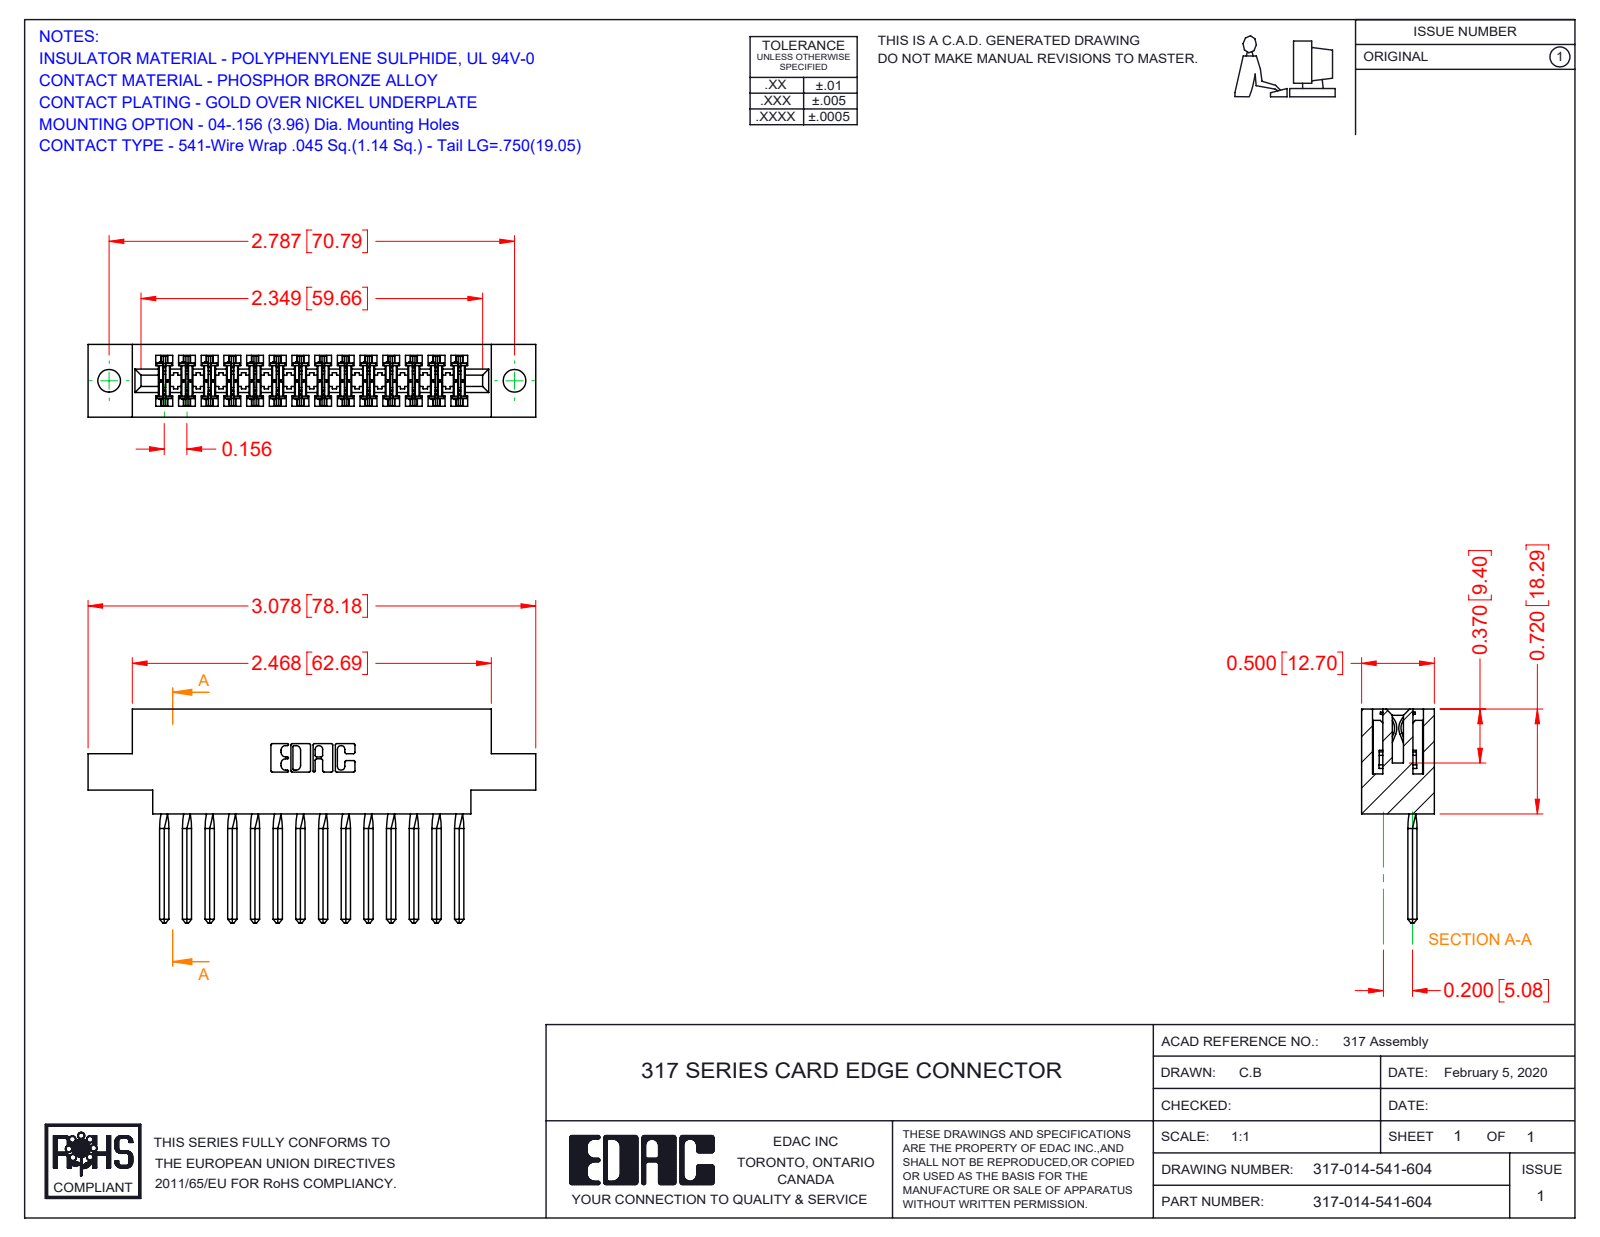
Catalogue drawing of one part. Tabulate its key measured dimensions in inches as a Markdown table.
| quantity | value |
| --- | --- |
| part name | 317 Part_.156 Dia - TH; 317-014-541-604; 317-290-002_541 |
| STEP written by | SolidWorks 2016 (CONFIG_CONTROL_DESIGN) |
| units | inches |
| bodies | 15 solids, 2230 faces (1794 planar, 380 cylindrical, 56 other) |
| overall size | 3.078 × 1.47 × 0.5 |
| volume | 0.716 in³ |
| surface area | 23.96 in² |
| round holes (diameter × count) | 0.156 × 2 |
| partial cylindrical surfaces (radius × count) | 0.015 × 28, 0.01 × 22, 0.007 × 6, 0.031 × 6, 0.026 × 3, 0.095 × 2, 0.1 × 2, 0.11 × 2 |
| main face-to-face distances | 0.5, 0.075, 0.425, 0.11, 0.22, 0.35, 0.065, 0.195, 0.331, 0.72 |
| hole center spacings | 2.787 |
